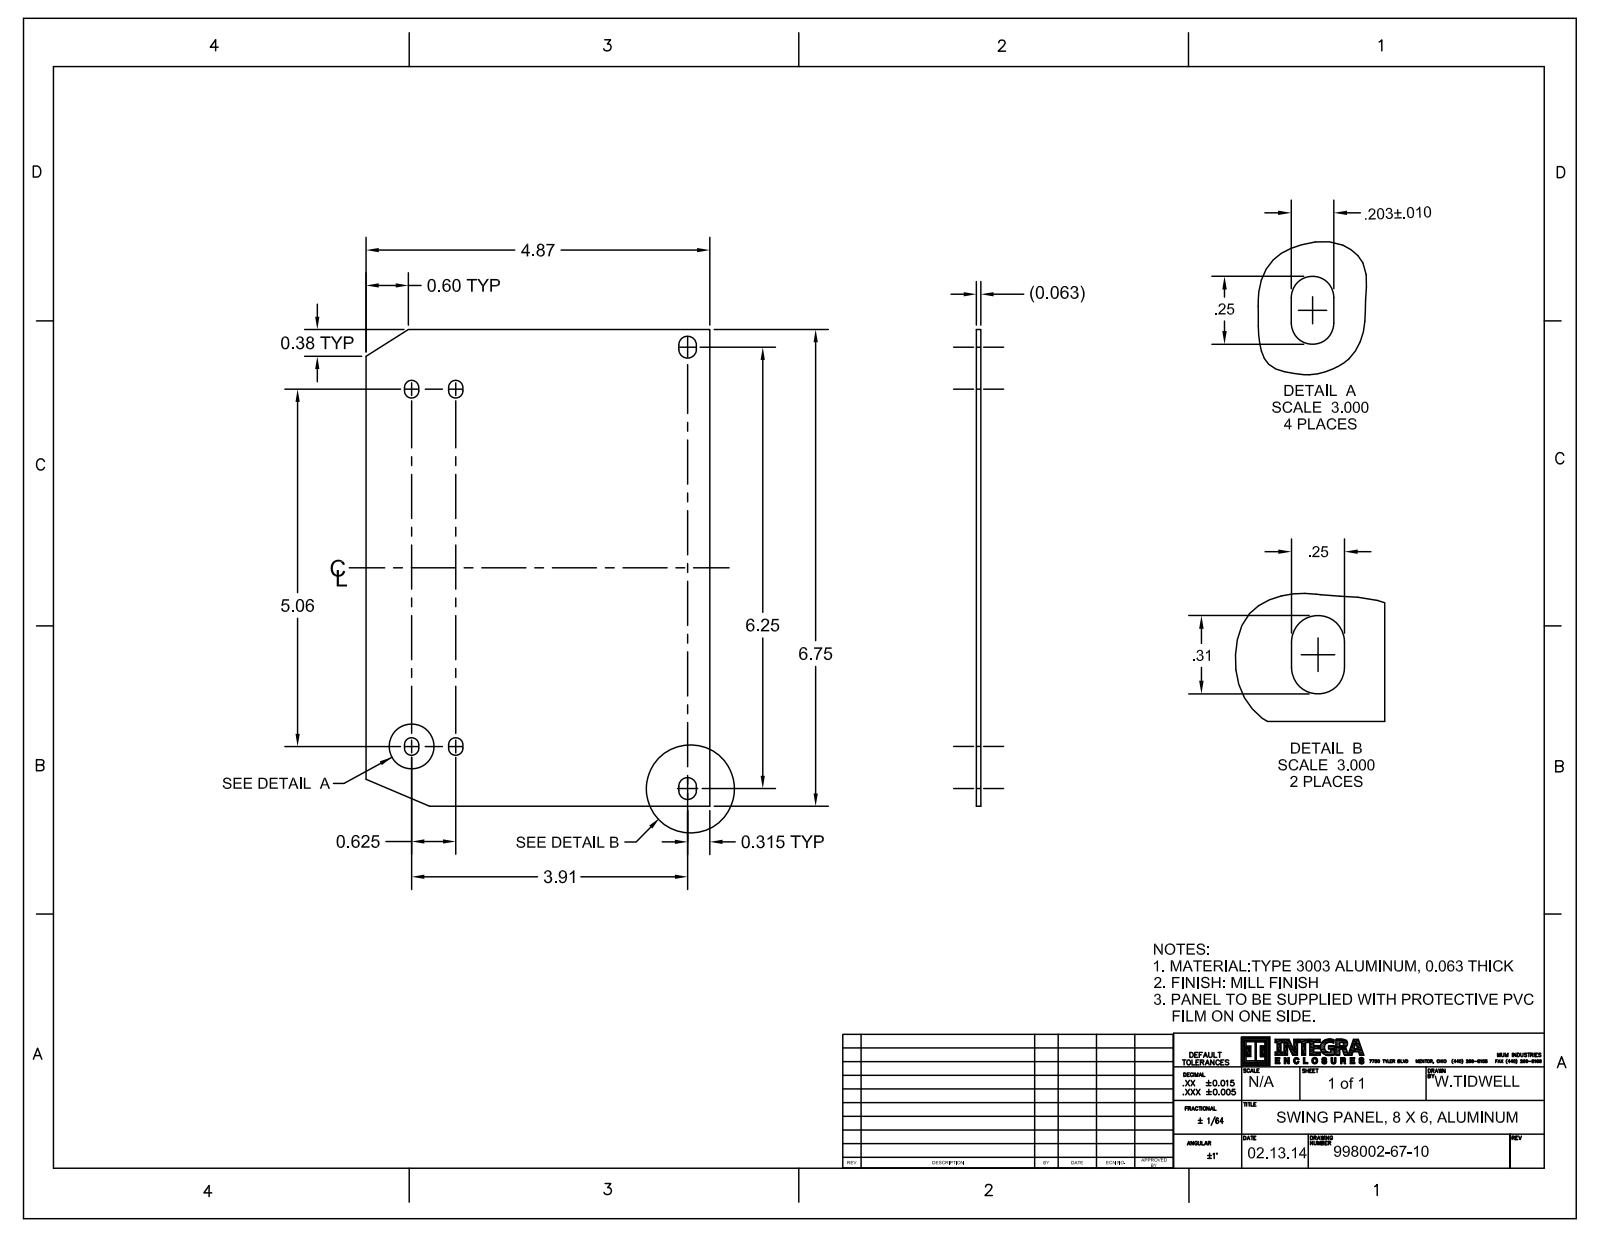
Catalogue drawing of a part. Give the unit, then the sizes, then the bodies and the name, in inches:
Units: inches
Overall size (bounding box): 7.738 × 5.731 × 1.609
Round holes (diameter × count): ⌀0.19 ×8, ⌀0.246 ×8, ⌀0.357 ×8, ⌀0.208 ×4, ⌀0.314 ×4, ⌀0.271 ×2
Round bosses / shafts (diameter × count): ⌀0.25 ×12, ⌀0.3 ×8, ⌀0.298 ×8, ⌀0.29 ×8, ⌀0.26 ×8, ⌀0.258 ×8, ⌀0.44 ×7, ⌀0.43 ×6
Partial cylindrical surfaces — rounded edges, fillets, slot ends (radius × count): R0.03 ×124, R0.004 ×48, R0.005 ×47, R0.05 ×38, R0.029 ×16, R0.046 ×16, R0.06 ×16, R0.02 ×14
Main face-to-face distances: 0.062, 0.046, 0.5, 0.38, 5.08, 0.11, 0.11, 1.2, 0.6, 5.58
Hole centre spacings: 0.625, 0.677, 1.13, 3.952, 4.25, 5.08, 5.118, 5.675
Volume: 5.057 in³ · Surface area: 116.9 in²
Bodies: 31 solids, 2116 faces (478 planar, 994 cylindrical, 644 other)
Part name (STEP PRODUCT): 9912511-20-50; 9912525-80-10; 9912511-20-50_ASM; 995008-20-90 (+8 more)
STEP written by: CREO PARAMETRIC BY PTC INC, 2016050 (CONFIG_CONTROL_DESIGN)
